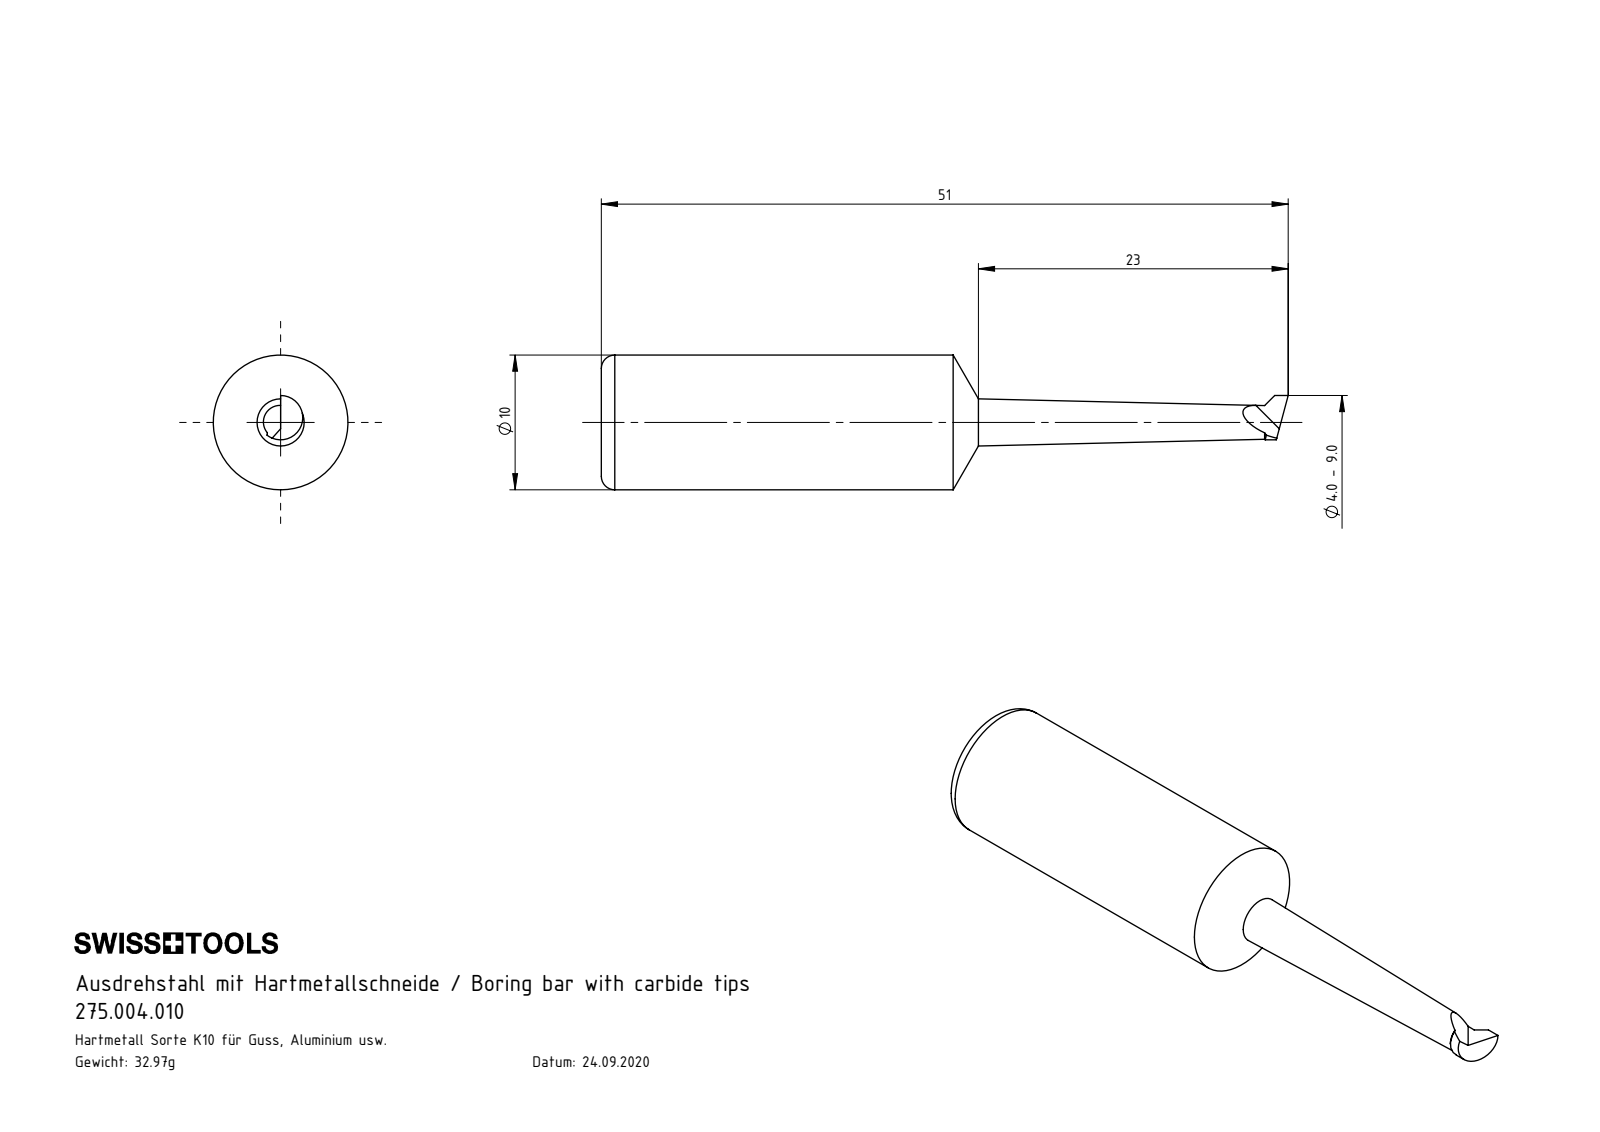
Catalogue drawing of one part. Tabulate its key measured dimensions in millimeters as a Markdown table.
| quantity | value |
| --- | --- |
| part name | 275.004.010 |
| STEP written by | SolidWorks 2022 (AUTOMOTIVE_DESIGN) |
| units | millimeters |
| bodies | 1 solid, 14 faces (4 planar, 3 cylindrical, 7 other) |
| overall size | 51 × 10 × 10 |
| volume | 2 274 mm³ |
| surface area | 1 182 mm² |
| round bosses / shafts (diameter × count) | 10 × 1 |
| partial cylindrical surfaces (radius × count) | 1.65 × 1 |
